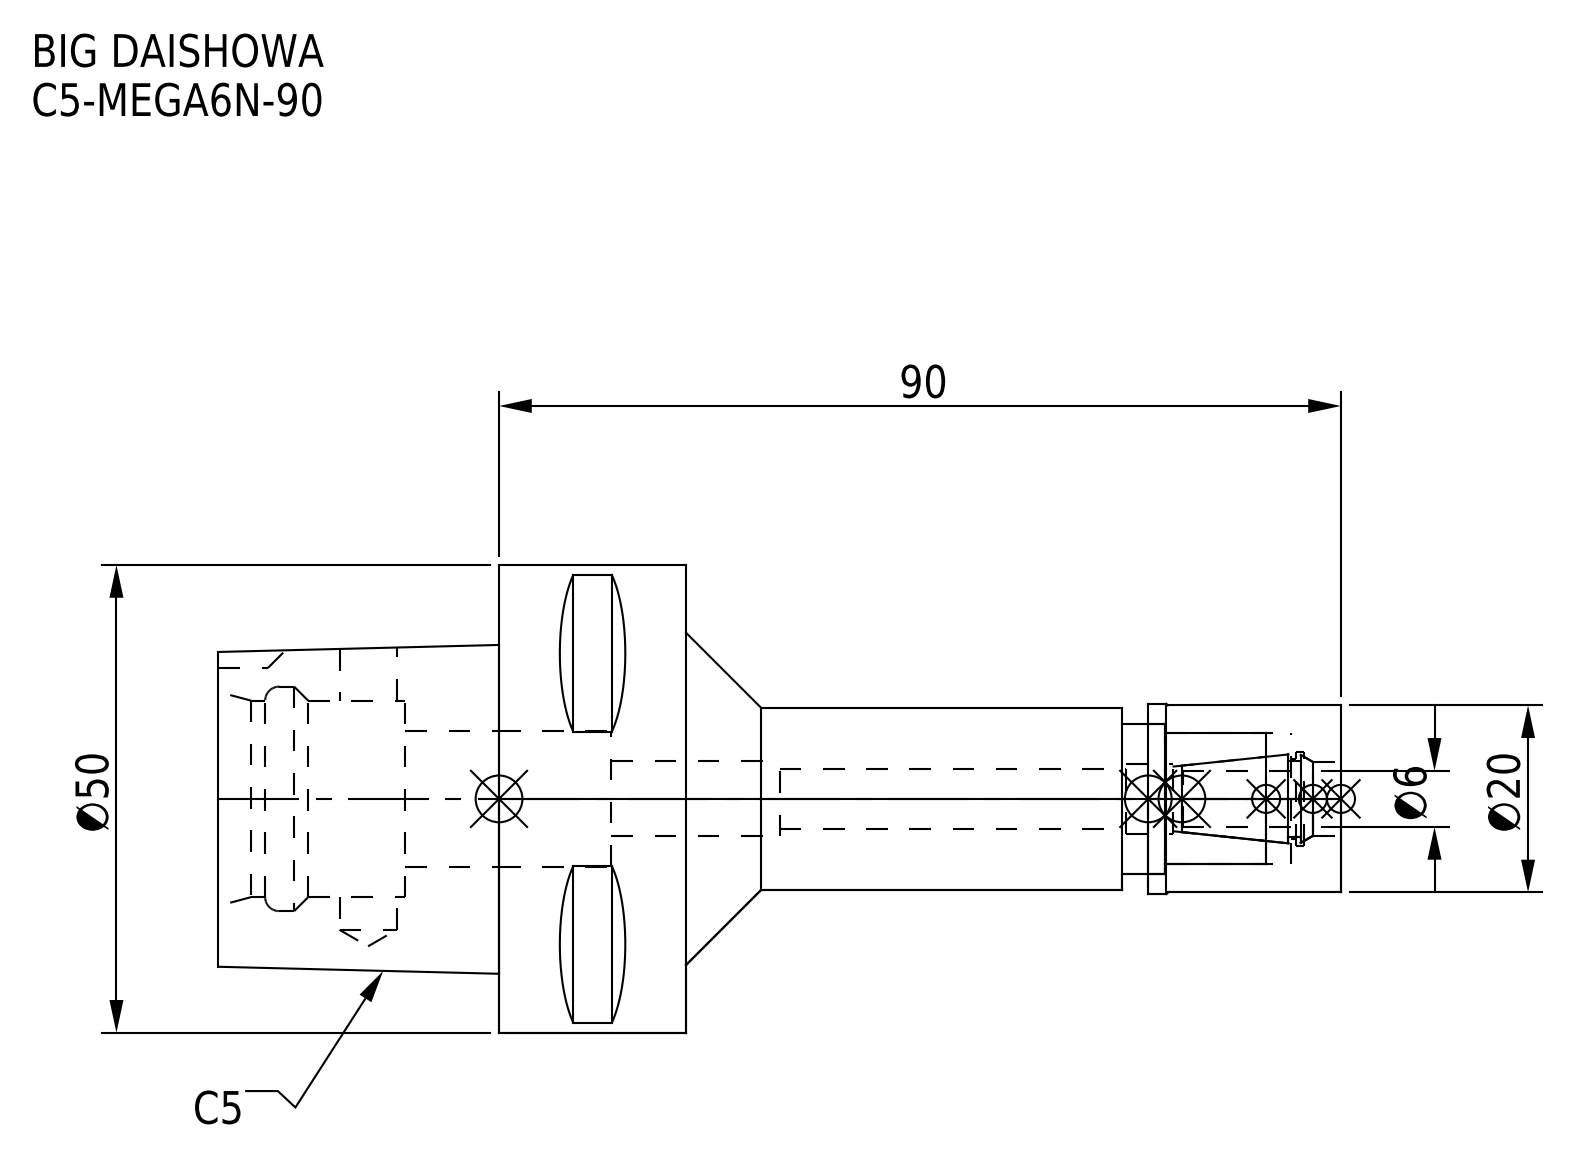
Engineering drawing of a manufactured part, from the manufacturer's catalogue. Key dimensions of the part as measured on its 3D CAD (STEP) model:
Part name (STEP PRODUCT): C5-MEGA6N-90; C5-MEGA6N-90-060-FreeParts; C5-MEGA6N-90-060_ASM.stp; DXF_TEMP_ASSY_ASM_4_ASM.stp (+3 more)
STEP written by: SolidWorks 2019 (CONFIG_CONTROL_DESIGN)
Units: millimetres
Bodies: 2 solids, 98 faces (39 planar, 41 cylindrical, 18 other)
Overall size (bounding box): 120 × 50 × 50
Volume: 74 435 mm³ · Surface area: 20 513 mm²
Round holes (diameter × count): ⌀6.1 ×1, ⌀6.4 ×1, ⌀7.5 ×1, ⌀7.9 ×1, ⌀8 ×1, ⌀8.5 ×1, ⌀10 ×1, ⌀14 ×1, ⌀14.5 ×1, ⌀16 ×1, ⌀21 ×1, ⌀24 ×1
Round bosses / shafts (diameter × count): ⌀50 ×1, ⌀20.3 ×1, ⌀20 ×1, ⌀19.5 ×1
Partial cylindrical surfaces — rounded edges, fillets, slot ends (radius × count): R4 ×1
Main face-to-face distances: 20, 30, 50, 70, 90, 120, 10, 8, 44, 100
